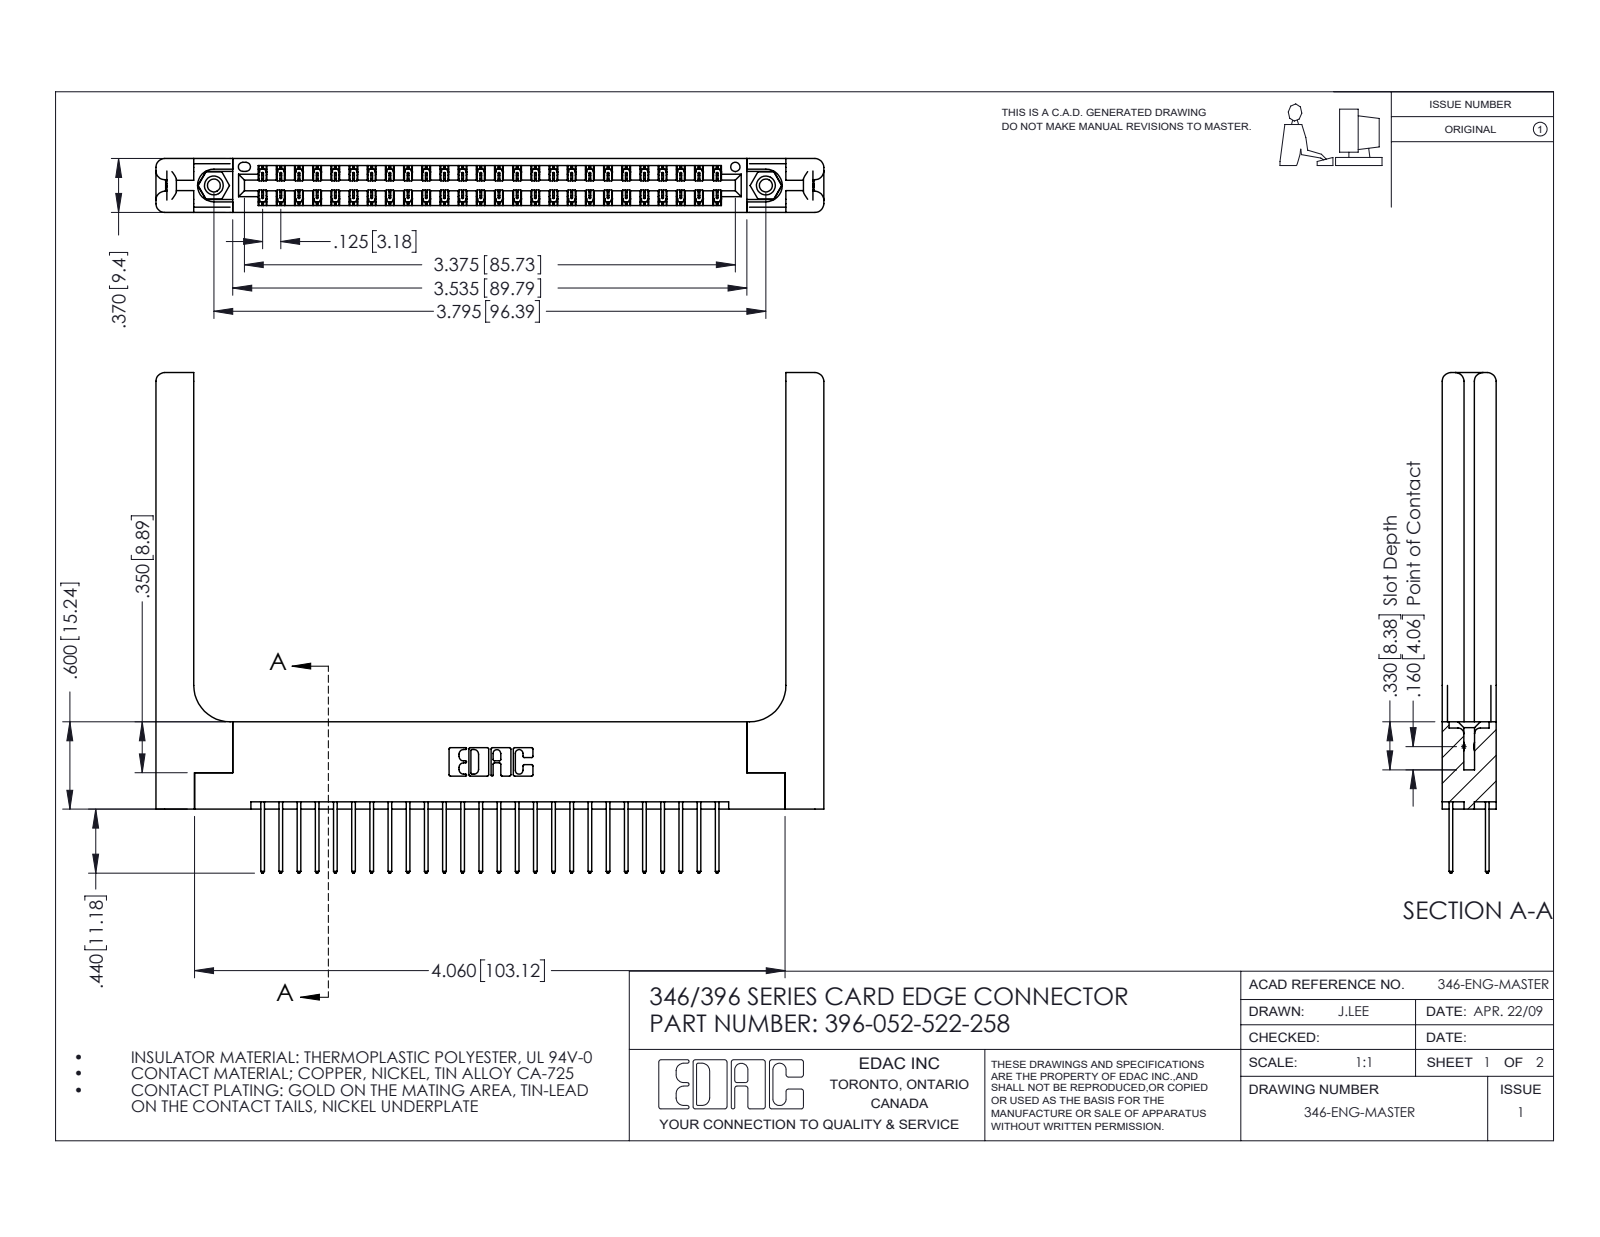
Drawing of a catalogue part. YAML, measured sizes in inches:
part_name: "345-292-001_345-293-122; 346 Part_Flush Mounting Lugs - 0.156 Dia-TH; 396-052-522-258; 346-220-058_345-220-058 (+1 more)"
step_written_by: "SolidWorks 2016 (CONFIG_CONTROL_DESIGN)"
units: inches
bodies: {solids: 57, faces: 3082, planar: 2044, cylindrical: 978, other: 60}
overall_size: [4.591, 3.44, 0.37]
volume: 1.152
surface_area: 32.52
round_holes:
  - {diameter: 0.089, count: 2}
  - {diameter: 0.125, count: 2}
  - {diameter: 0.156, count: 2}
  - {diameter: 0.064, count: 1}
round_bosses_or_shafts:
  - {diameter: 0.155, count: 2}
partial_cylinders:
  - {radius: 0.006, count: 78}
  - {radius: 0.01, count: 52}
  - {radius: 0.01, count: 22}
  - {radius: 0.06, count: 16}
  - {radius: 0.007, count: 6}
  - {radius: 0.031, count: 6}
  - {radius: 0.026, count: 3}
  - {radius: 0.014, count: 2}
face_to_face_distances: [0.37, 0.072, 0.048, 0.322, 0.25, 0.148, 0.15, 0.025, 0.298, 0.275]
hole_center_spacings: [0.246, 3.587, 3.795]
